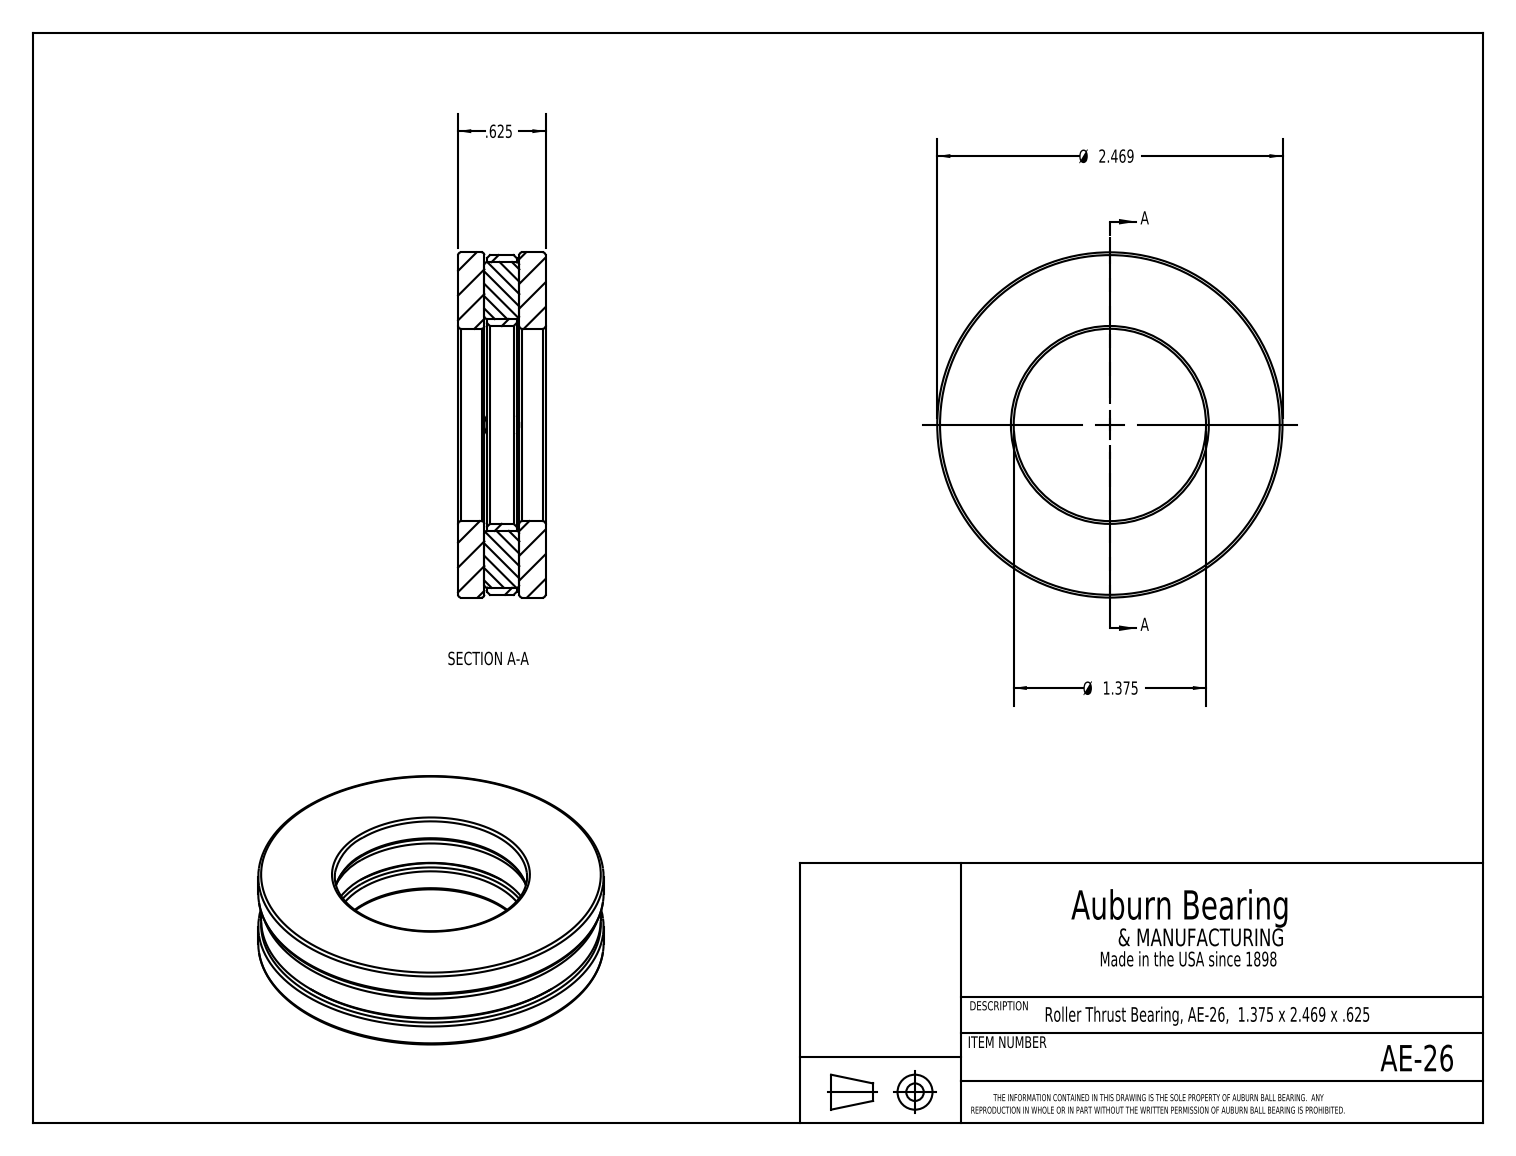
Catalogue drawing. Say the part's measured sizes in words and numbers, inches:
The part is named "AE-26". Its 3-D file was written by "SolidWorks 2017 (CONFIG_CONTROL_DESIGN)". It is 7 solids with 60 faces: 30 planar, 10 cylindrical and 20 other. Overall it measures 2.469 by 2.469 by 0.625 inches. Its volume is 1.866 cubic inches and its surface area 27.6 square inches. Round holes: 1 of diameter 1.375, 1 of diameter 1.415. Round bosses or shafts: 2 of diameter 0.25, 1 of diameter 2.469, 1 of diameter 2.429. The main face-to-face distances are 0.207, 0.418, 0.25, 0.187, 0.437, 0.625, 0.438, 0.188, 0.23, 0.02.
